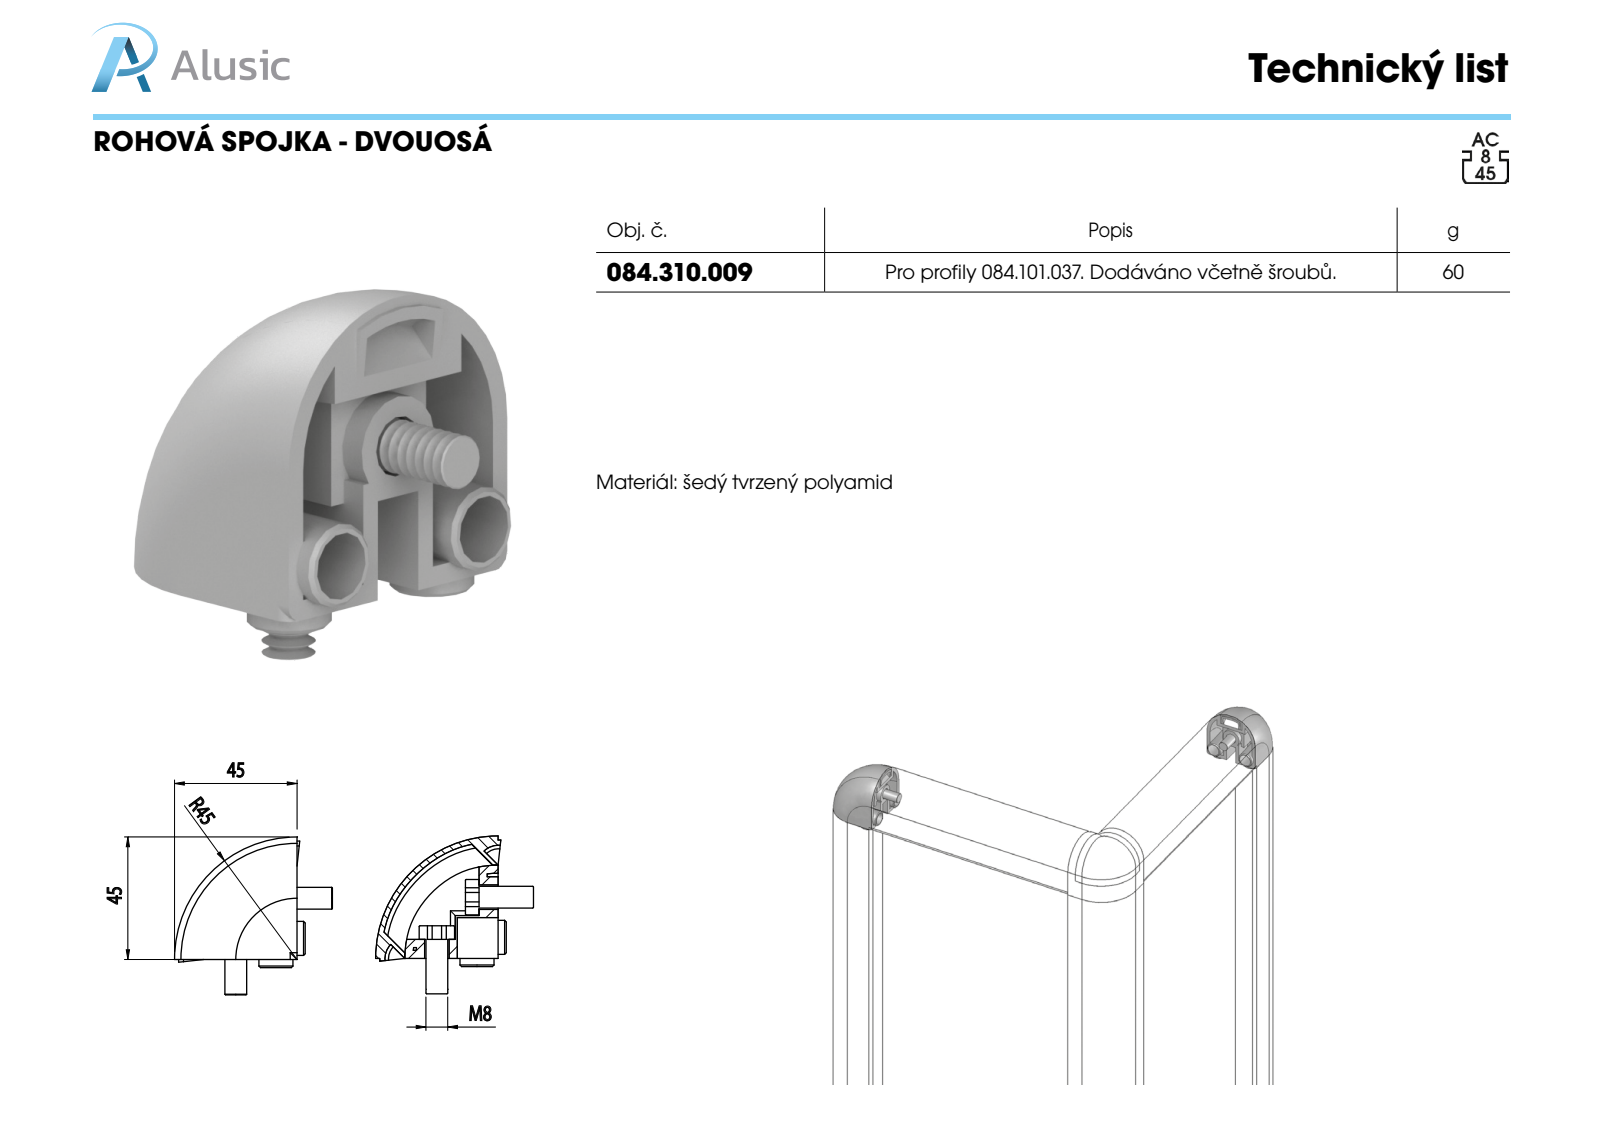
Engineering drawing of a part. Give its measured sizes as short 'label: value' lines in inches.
name: 084.310.009-1; 084.310.009; 084.310.009-2; 084.301.000 VITI ALUSIC_084.301.003
written by: SolidWorks 2011 (CONFIG_CONTROL_DESIGN)
unit: in
bodies: 4 solids, 182 faces (102 planar, 56 cylindrical, 24 other)
size: 2.283 × 2.283 × 1.772
volume: 1.964 in³; area: 39.11 in²
holes: 4× ⌀0.394, 2× ⌀0.256, 2× ⌀0.354
bosses: 4× ⌀0.492, 2× ⌀0.512, 2× ⌀0.315
rounds: 4× R0.098, 2× R0.266, 2× R0.295, 2× R0.827, 1× R1.232, 1× R1.35
face distances: 0.118, 0.128, 0.778, 0.787, 1.28, 1.152, 0.502, 0.197, 0.374, 0.492
hole spacings: 0.819, 1.154
